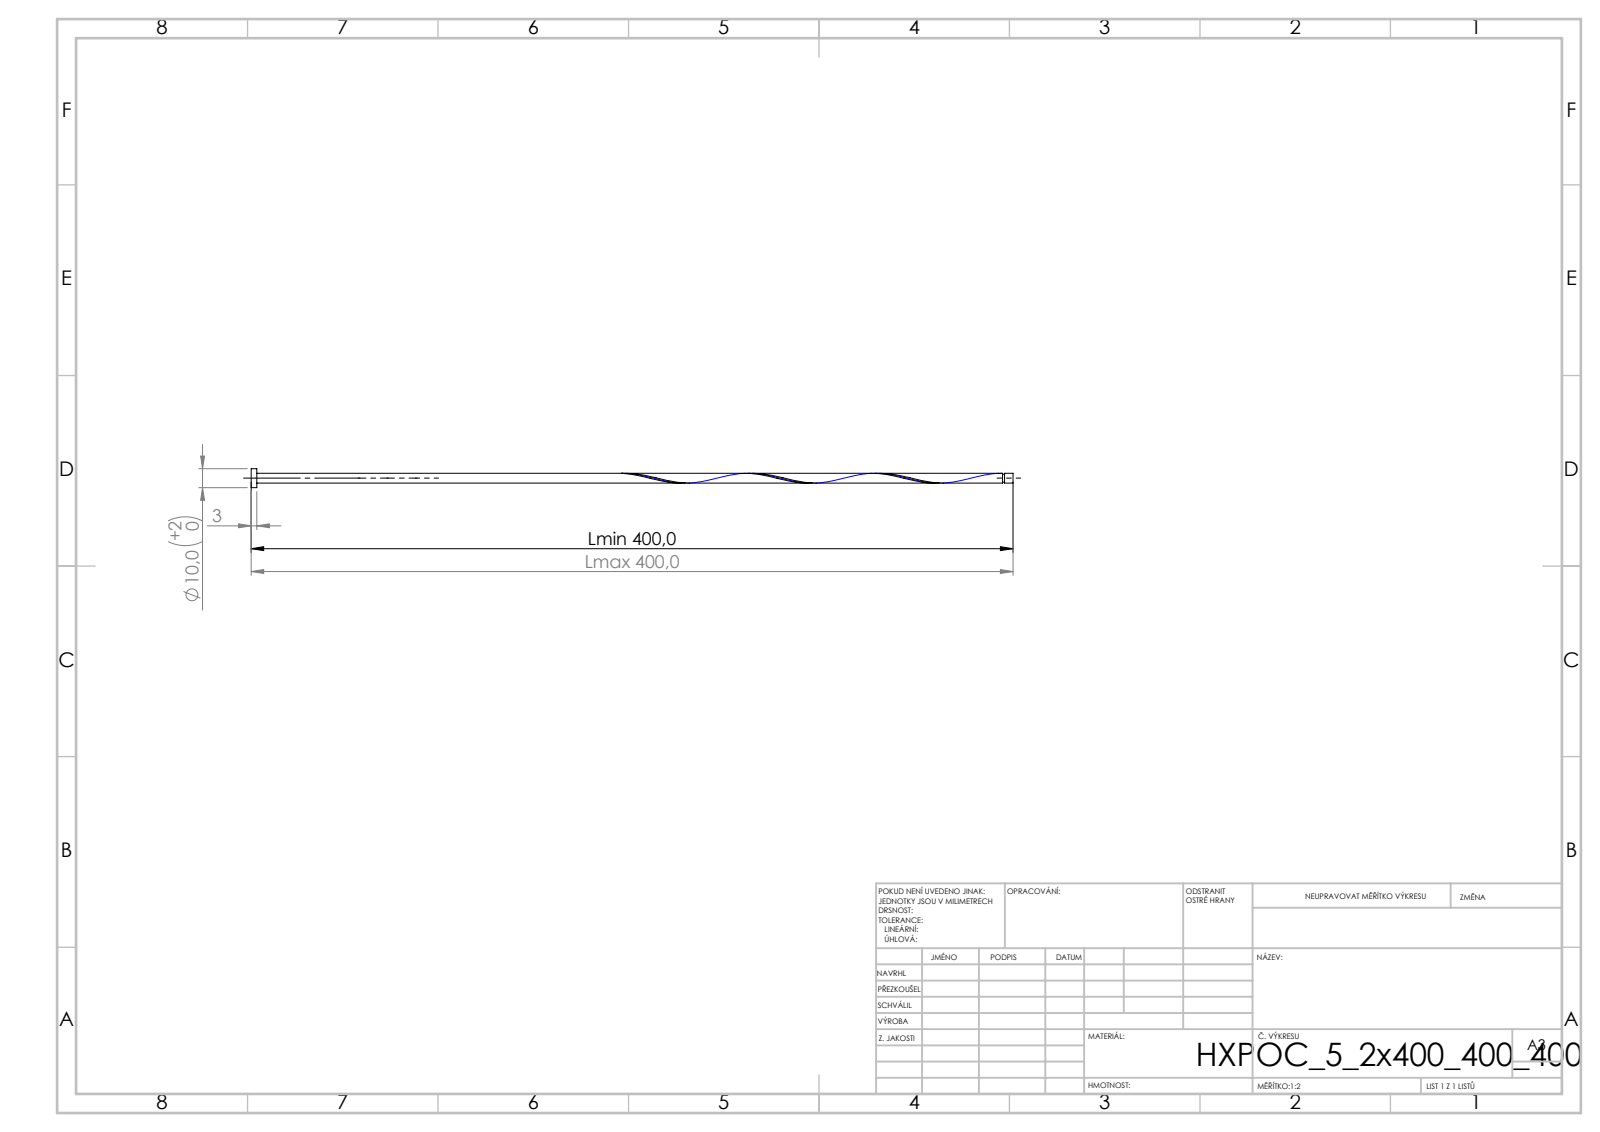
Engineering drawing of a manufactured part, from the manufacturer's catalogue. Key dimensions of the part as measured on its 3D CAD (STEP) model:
STEP written by: SolidWorks 2019 (CONFIG_CONTROL_DESIGN)
Units: millimetres
Bodies: 1 solid, 16 faces (6 planar, 9 cylindrical, 1 other)
Overall size (bounding box): 400 × 10 × 10
Volume: 10 466 mm³ · Surface area: 9 030 mm²
Round bosses / shafts (diameter × count): ⌀10 ×1, ⌀5.2 ×1, ⌀4.16 ×1
Main face-to-face distances: 3, 400, 397, 395.56, 392.56, 4.44, 394.52, 391.52, 1.04, 5.48
